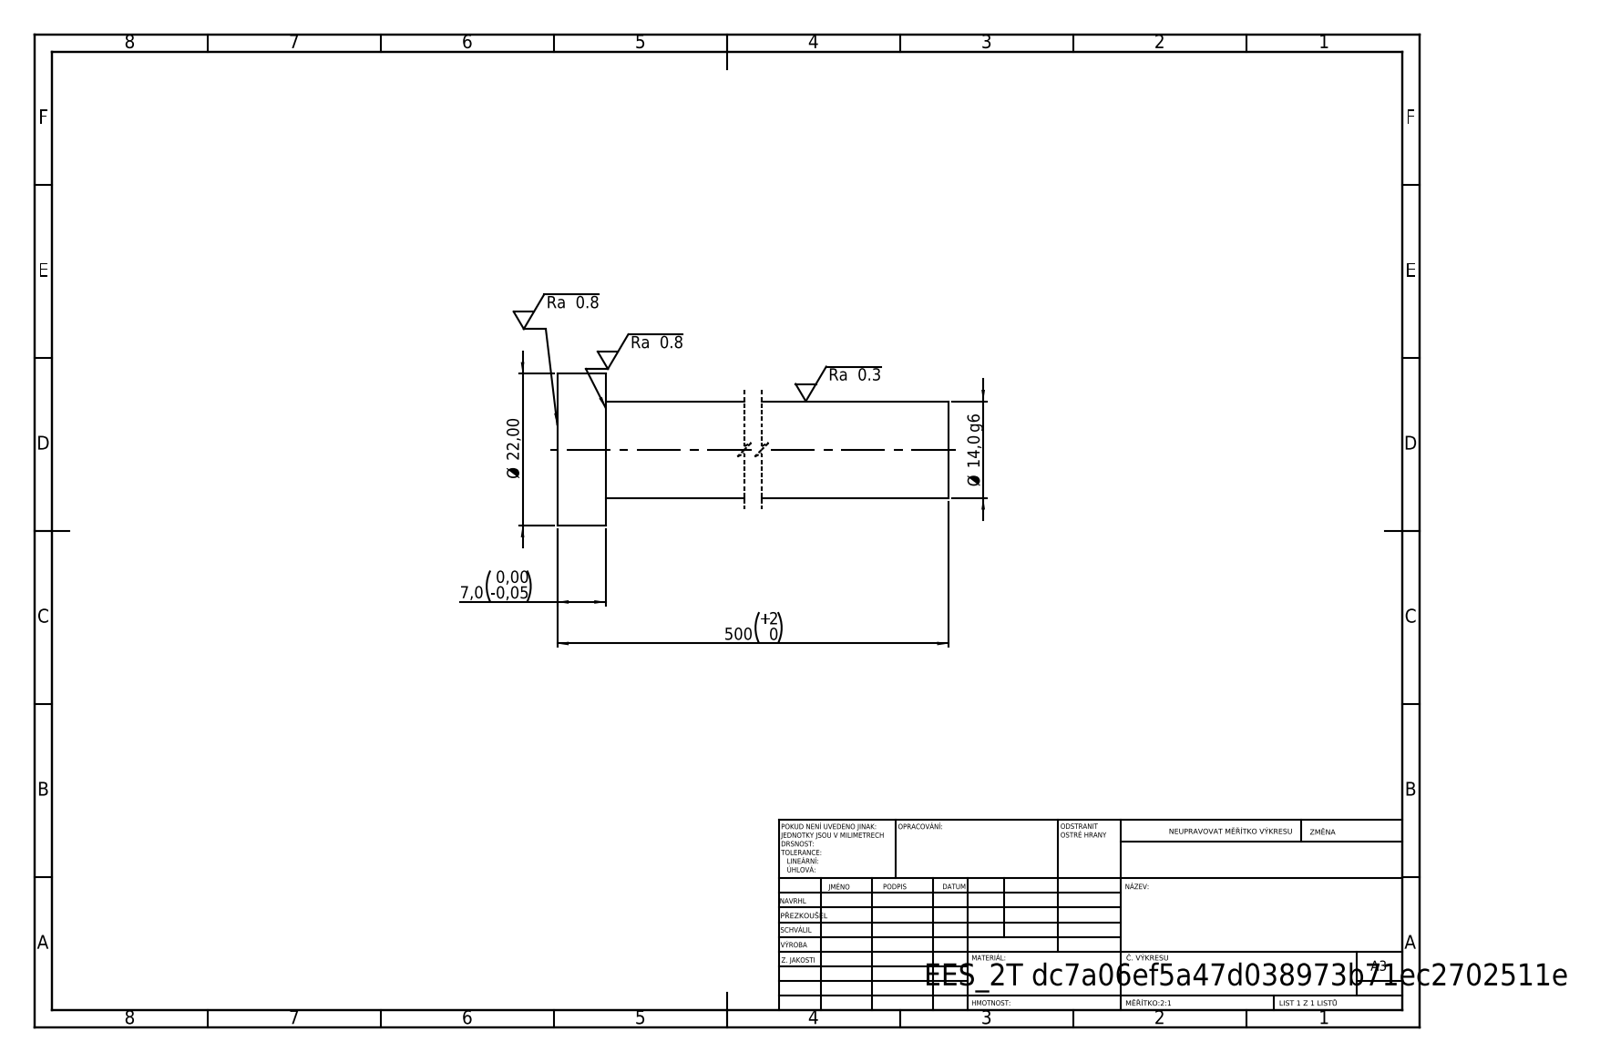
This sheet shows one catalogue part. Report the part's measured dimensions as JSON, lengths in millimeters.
{"step_written_by": "SolidWorks 2019 (CONFIG_CONTROL_DESIGN)", "units": "millimeters", "bodies": {"solids": 1, "faces": 7, "planar": 3, "cylindrical": 4, "other": 0}, "overall_size": [500, 22, 22], "volume_mm3": 78552, "surface_area_mm2": 22927, "round_bosses_or_shafts": [[22, 1], [14, 1]], "face_to_face_distances": [7, 500, 493]}
